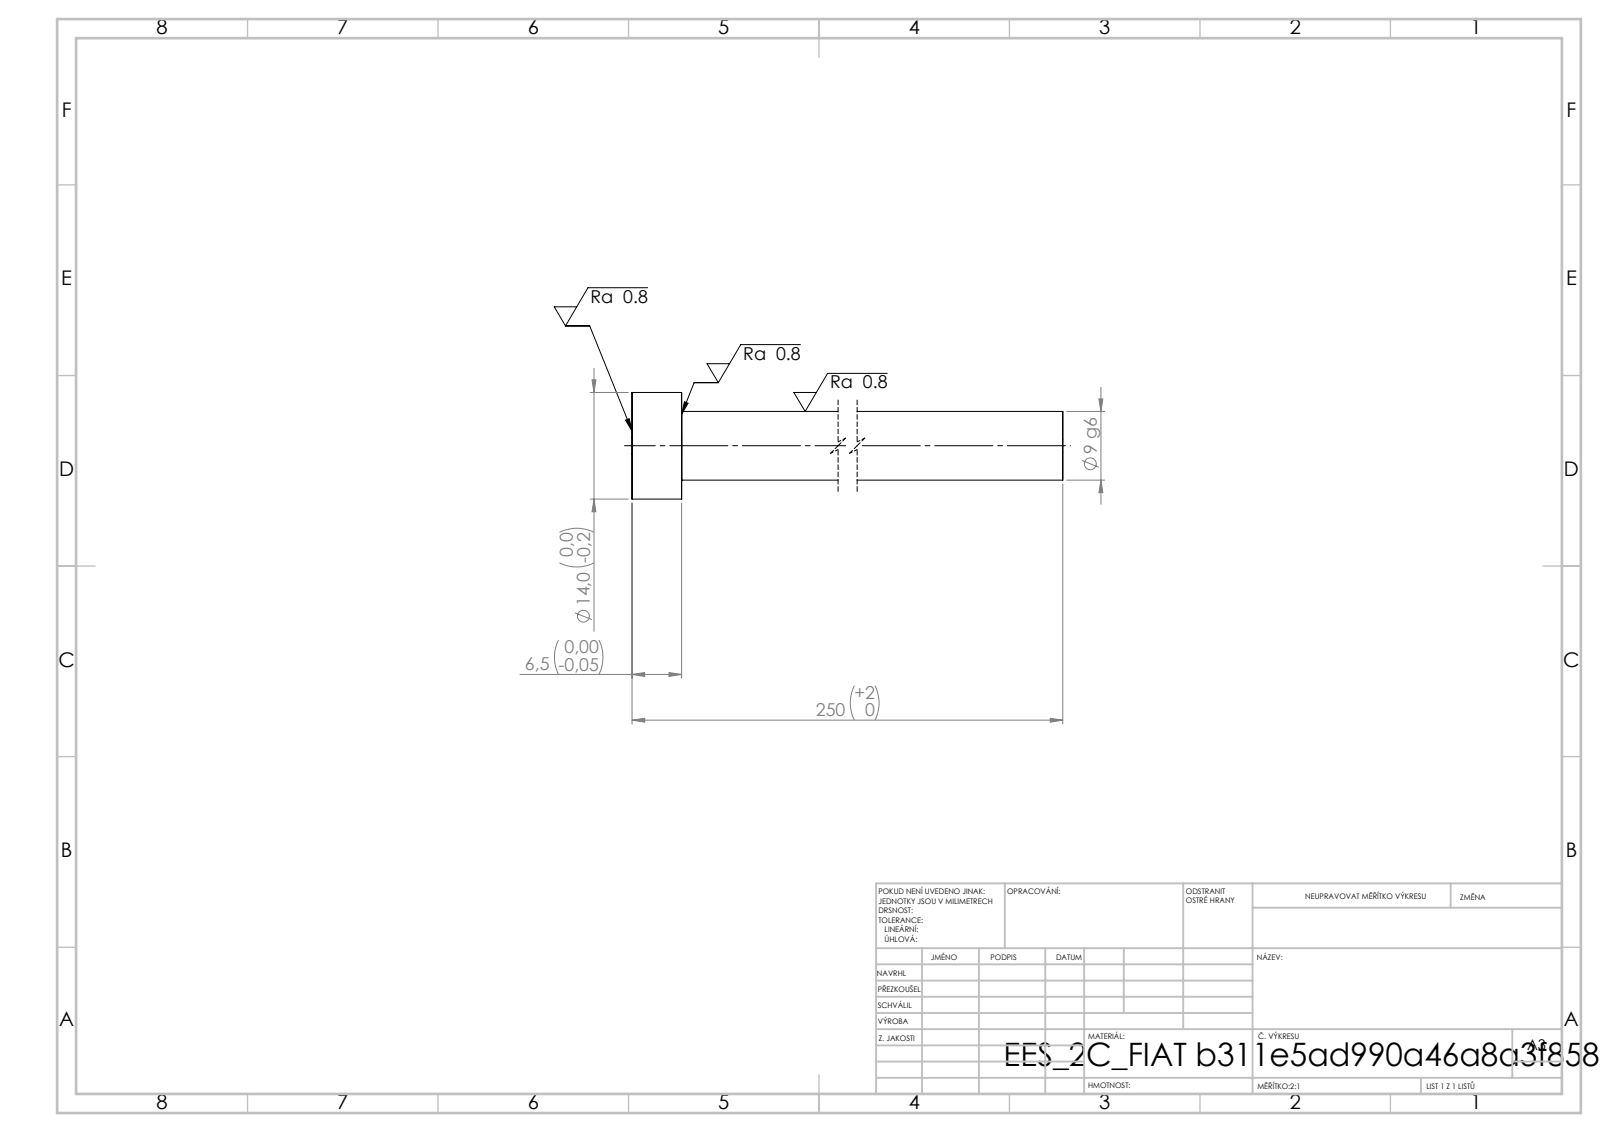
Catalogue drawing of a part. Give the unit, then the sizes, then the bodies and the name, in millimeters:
Units: millimetres
Overall size (bounding box): 250 × 14 × 14
Round bosses / shafts (diameter × count): ⌀14 ×1, ⌀9 ×1
Main face-to-face distances: 6.5, 250, 243.5
Volume: 16 491 mm³ · Surface area: 7 479 mm²
Bodies: 1 solid, 7 faces (3 planar, 4 cylindrical, 0 other)
STEP written by: SolidWorks 2019 (CONFIG_CONTROL_DESIGN)
